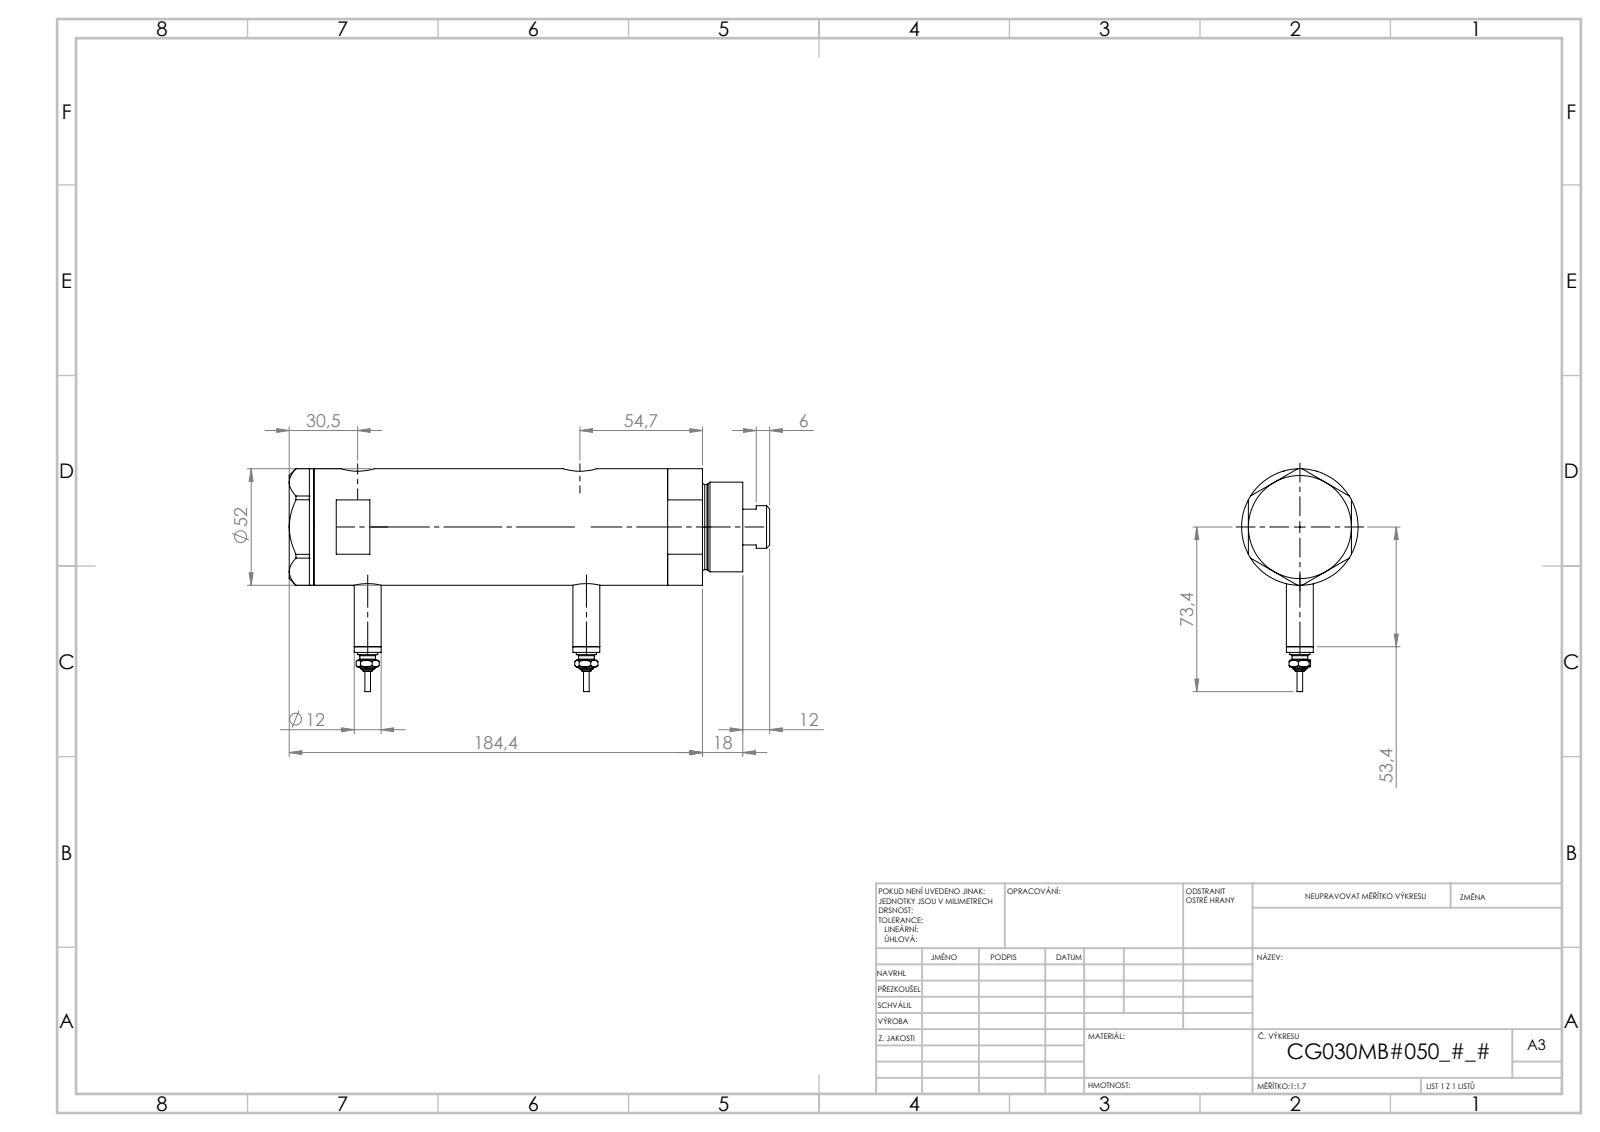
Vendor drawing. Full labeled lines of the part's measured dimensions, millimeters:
Part name (STEP PRODUCT): V270CG_VC; V270CG_BACK; V270CG_FRONT; Switch (+1 more)
STEP written by: SolidWorks 2019 (CONFIG_CONTROL_DESIGN)
Units: millimetres
Bodies: 6 solids, 226 faces (93 planar, 69 cylindrical, 64 other)
Overall size (bounding box): 214.4 × 99.4 × 52
Volume: 396 792 mm³ · Surface area: 89 841 mm²
Round holes (diameter × count): ⌀9.73 ×2, ⌀12.5 ×2, ⌀15 ×2, ⌀6.5 ×1, ⌀20 ×1, ⌀21.5 ×1, ⌀30 ×1, ⌀33 ×1, ⌀44 ×1
Round bosses / shafts (diameter × count): ⌀12 ×2, ⌀9 ×2, ⌀7 ×2, ⌀4.5 ×2, ⌀2.5 ×2, ⌀52 ×1, ⌀40 ×1, ⌀38 ×1
Main face-to-face distances: 121.5, 23.8, 97.7, 11, 34.8, 132.5, 46, 36.4, 168.9, 157.9
Hole centre spacings: 2.9, 4.5, 94.7, 97.6, 99.2, 102.1
